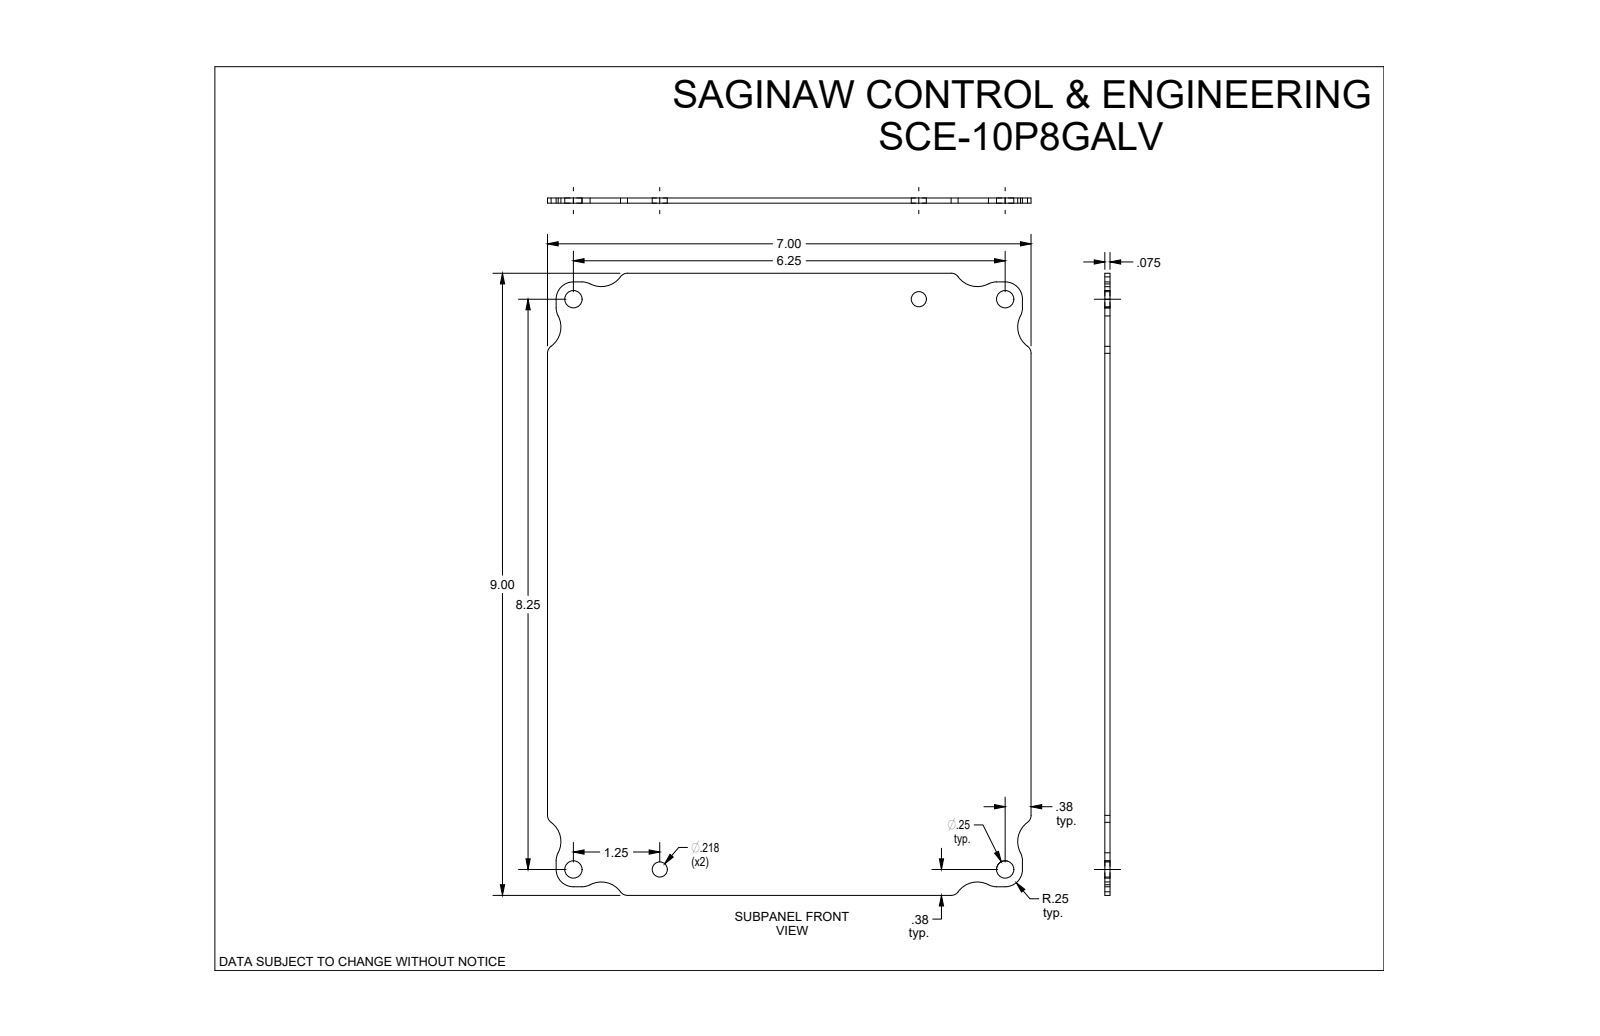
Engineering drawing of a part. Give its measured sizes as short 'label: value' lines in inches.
name: SCE-10P8AL
written by: SolidWorks 2019 (CONFIG_CONTROL_DESIGN)
unit: in
bodies: 1 solid, 48 faces (14 planar, 34 cylindrical, 0 other)
size: 9 × 7 × 0.08
volume: 4.922 in³; area: 125.9 in²
holes: 4× ⌀0.25, 2× ⌀0.218
rounds: 12× R0.25, 8× R0.125, 8× R0.344
face distances: 0.08, 7, 9, 0.125, 8.875, 6.875, 8.75, 6.75
hole spacings: 1.25, 5, 6.25, 8.25, 8.344, 9.646, 10.35, 9.062
